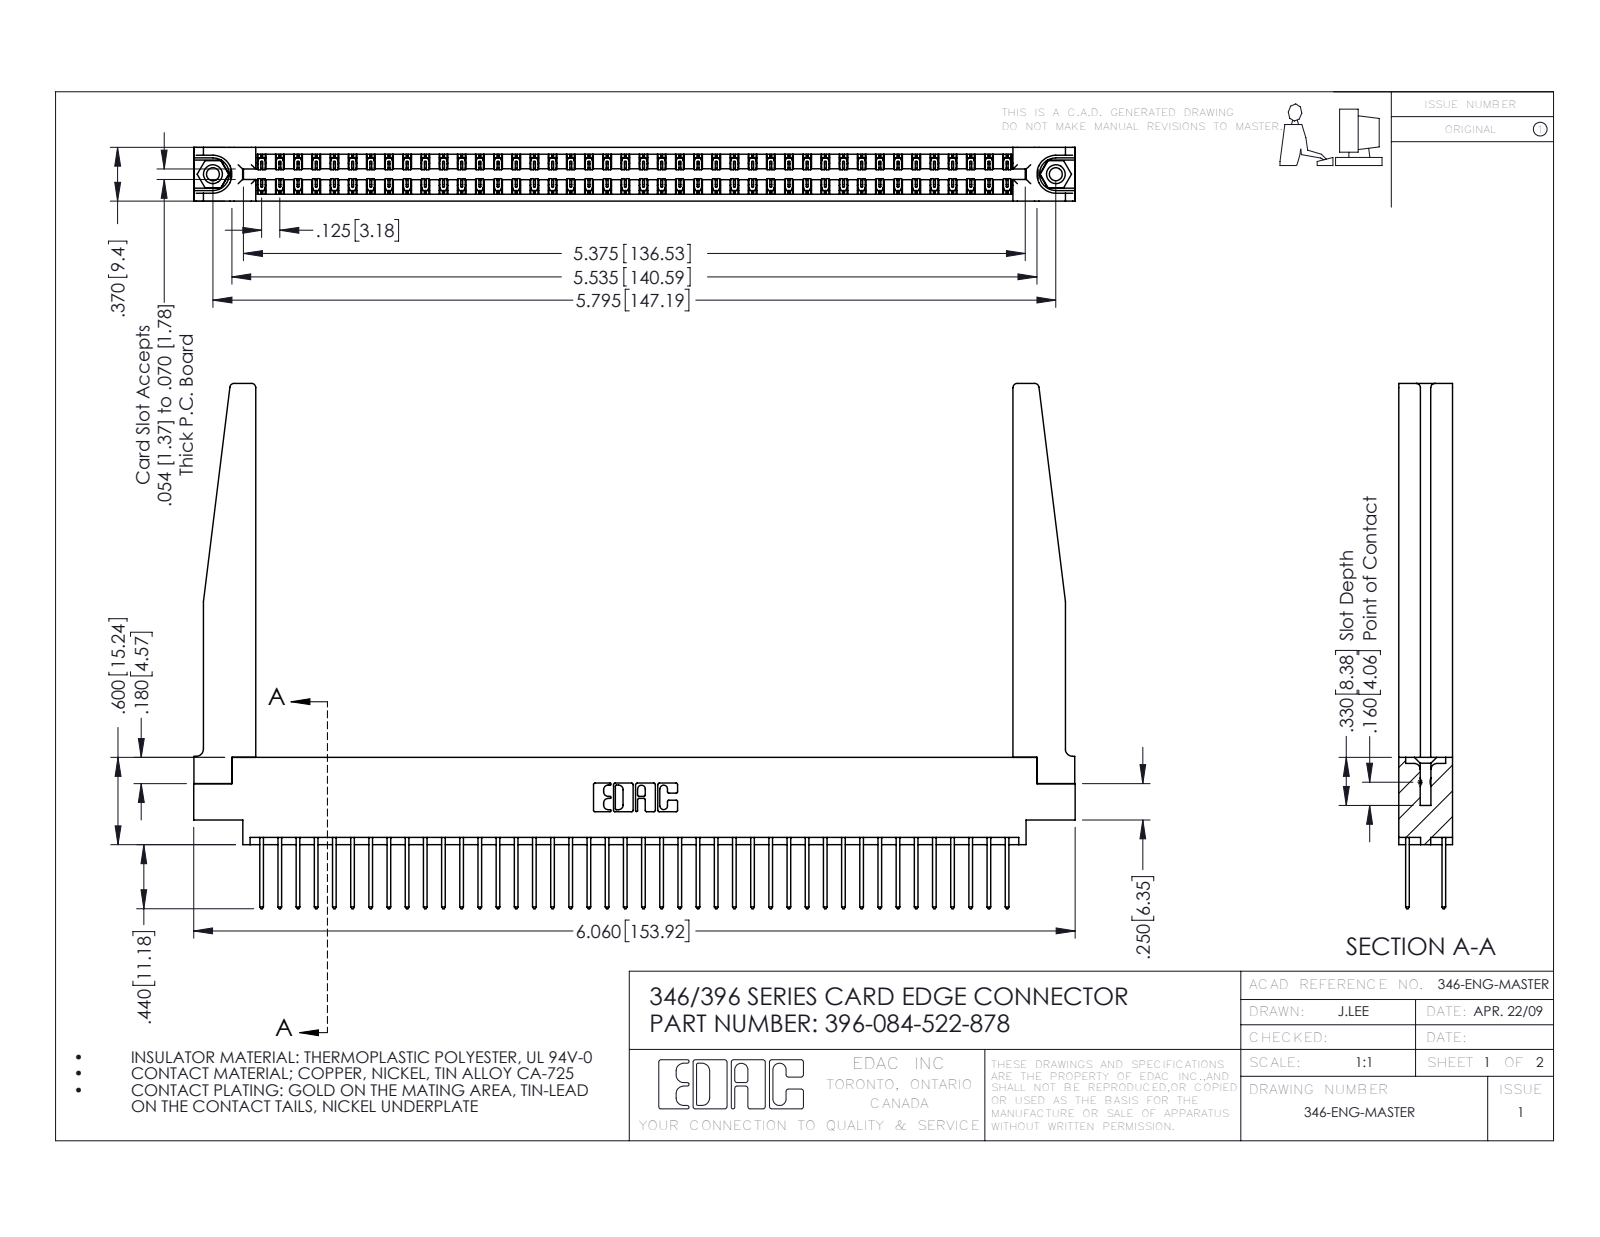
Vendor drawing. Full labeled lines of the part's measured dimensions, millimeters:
Part name (STEP PRODUCT): 345-250-001_345-250-001-102; 346 Part_0.170 Offset - 0.156 Dia-TH; 345-292-001_345-293-122; 346-220-078_345-220-078 (+1 more)
STEP written by: SolidWorks 2016 (CONFIG_CONTROL_DESIGN)
Units: millimetres
Bodies: 89 solids, 4728 faces (3162 planar, 1514 cylindrical, 52 other)
Overall size (bounding box): 153.9 × 91.7 × 9.4
Volume: 21 980 mm³ · Surface area: 28 430 mm²
Round holes (diameter × count): ⌀2.3 ×2, ⌀3.2 ×2, ⌀4 ×2, ⌀1.6 ×1
Round bosses / shafts (diameter × count): ⌀3.9 ×2
Partial cylindrical surfaces — rounded edges, fillets, slot ends (radius × count): R0.2 ×126, R0.3 ×84, R0.3 ×22, R0.8 ×8, R0.2 ×6, R0.8 ×6, R0.7 ×3, R0.4 ×2
Main face-to-face distances: 1.2, 8.2, 9.4, 1.8, 6.4, 7.6, 0.6, 3.8, 3.8, 7
Hole centre spacings: 6.2, 141.9, 147.2
